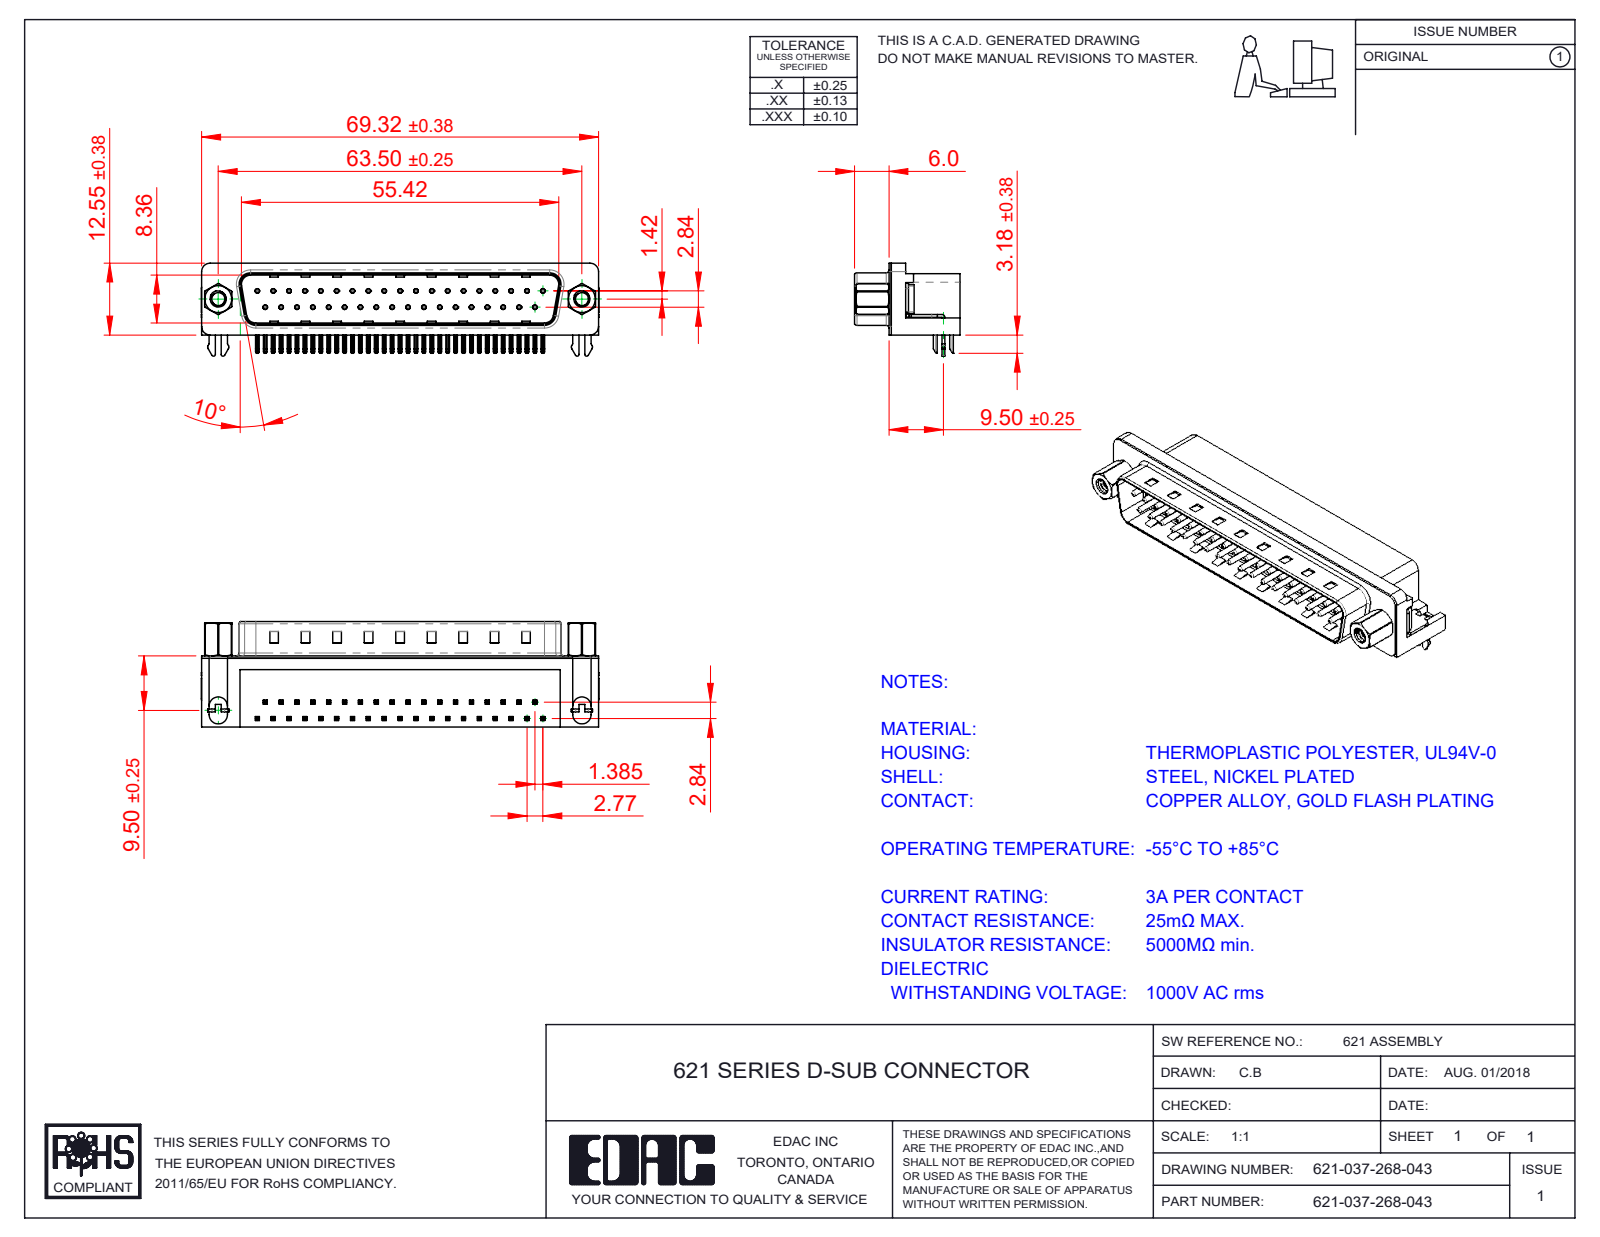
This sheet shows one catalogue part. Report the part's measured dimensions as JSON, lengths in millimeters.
{"part_name": "621 4-40 Hex Standoff 5; 621 4-40 Threaded Rivet; 621 Contact Bottom; 621 4 Prong Board Lock (+4 more)", "step_written_by": "SolidWorks 2016 (CONFIG_CONTROL_DESIGN)", "units": "millimeters", "bodies": {"solids": 45, "faces": 3445, "planar": 2077, "cylindrical": 993, "other": 375}, "overall_size": [69.4, 18.4, 16.25], "volume_mm3": 8844, "surface_area_mm2": 10652, "round_holes": [[0.35, 37], [0.8, 37], [2, 2], [2.26, 2], [2.29, 2], [4, 2], [4.8, 2], [5, 2]], "round_bosses_or_shafts": [[0.75, 37], [4.9, 2], [4.75, 2], [3.9, 2], [3, 2], [2.79, 2]], "partial_cylinders_radius": [[0.25, 160], [0.12, 74], [1, 16], [0.5, 9], [1.6, 8], [1.5, 7], [0.9, 4], [2, 4]], "face_to_face_distances": [0.4, 12, 10.35, 8.76, 2.1, 1.7, 10.46, 10.86, 12.4, 9], "hole_center_spacings": [3.16, 2.77, 5.54, 8.31, 11.08, 13.85, 19.39, 22.16]}
